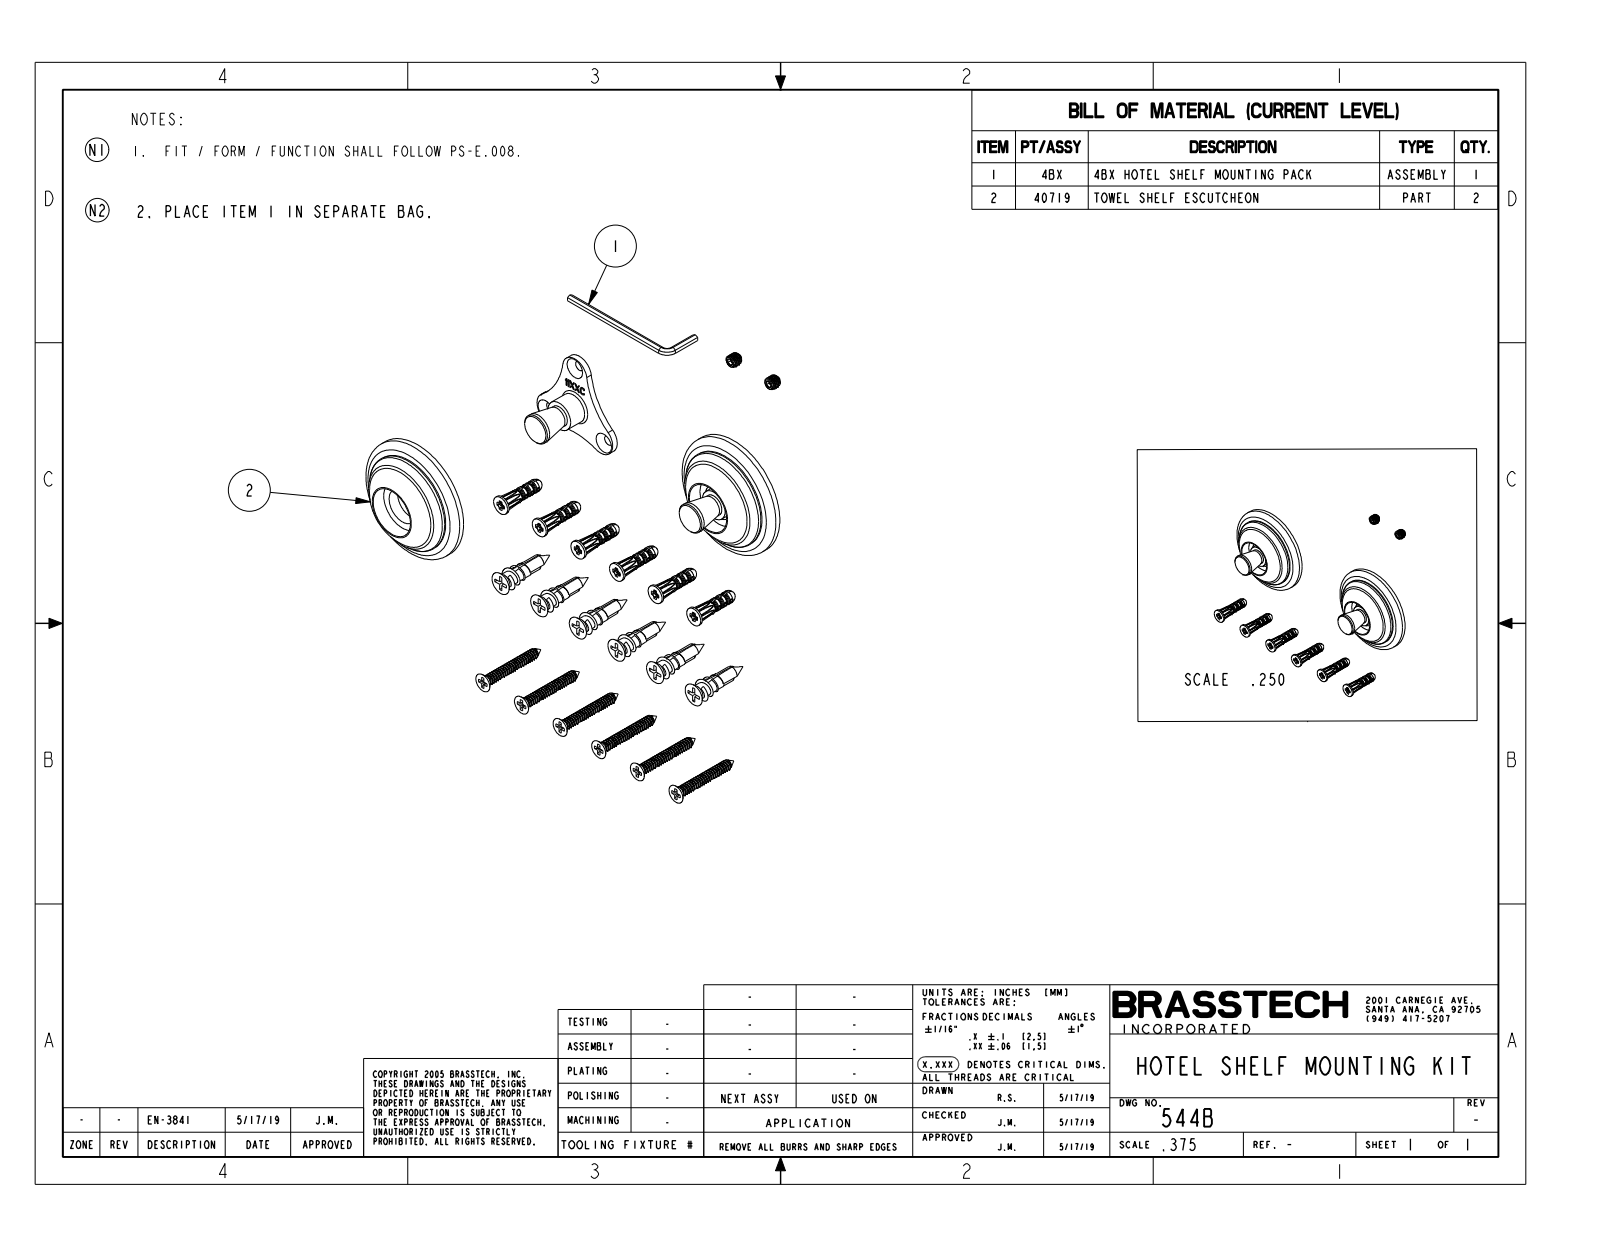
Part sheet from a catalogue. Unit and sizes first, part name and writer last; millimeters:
Units: millimetres
Overall size (bounding box): 161.9 × 60.3 × 17
Round holes (diameter × count): ⌀17.5 ×2, ⌀24.5 ×2, ⌀56.4 ×2
Round bosses / shafts (diameter × count): ⌀60.3 ×2
Main face-to-face distances: 1.3, 4.4, 5.7, 10, 5.6, 4.3, 17, 12.6, 11.3, 7
Hole centre spacings: 101.6
Volume: 29 790 mm³ · Surface area: 16 850 mm²
Bodies: 2 solids, 50 faces (10 planar, 16 cylindrical, 24 other)
Part name (STEP PRODUCT): 40719; 544B_ASM
STEP written by: CREO PARAMETRIC BY PTC INC, 2018400 (CONFIG_CONTROL_DESIGN)
